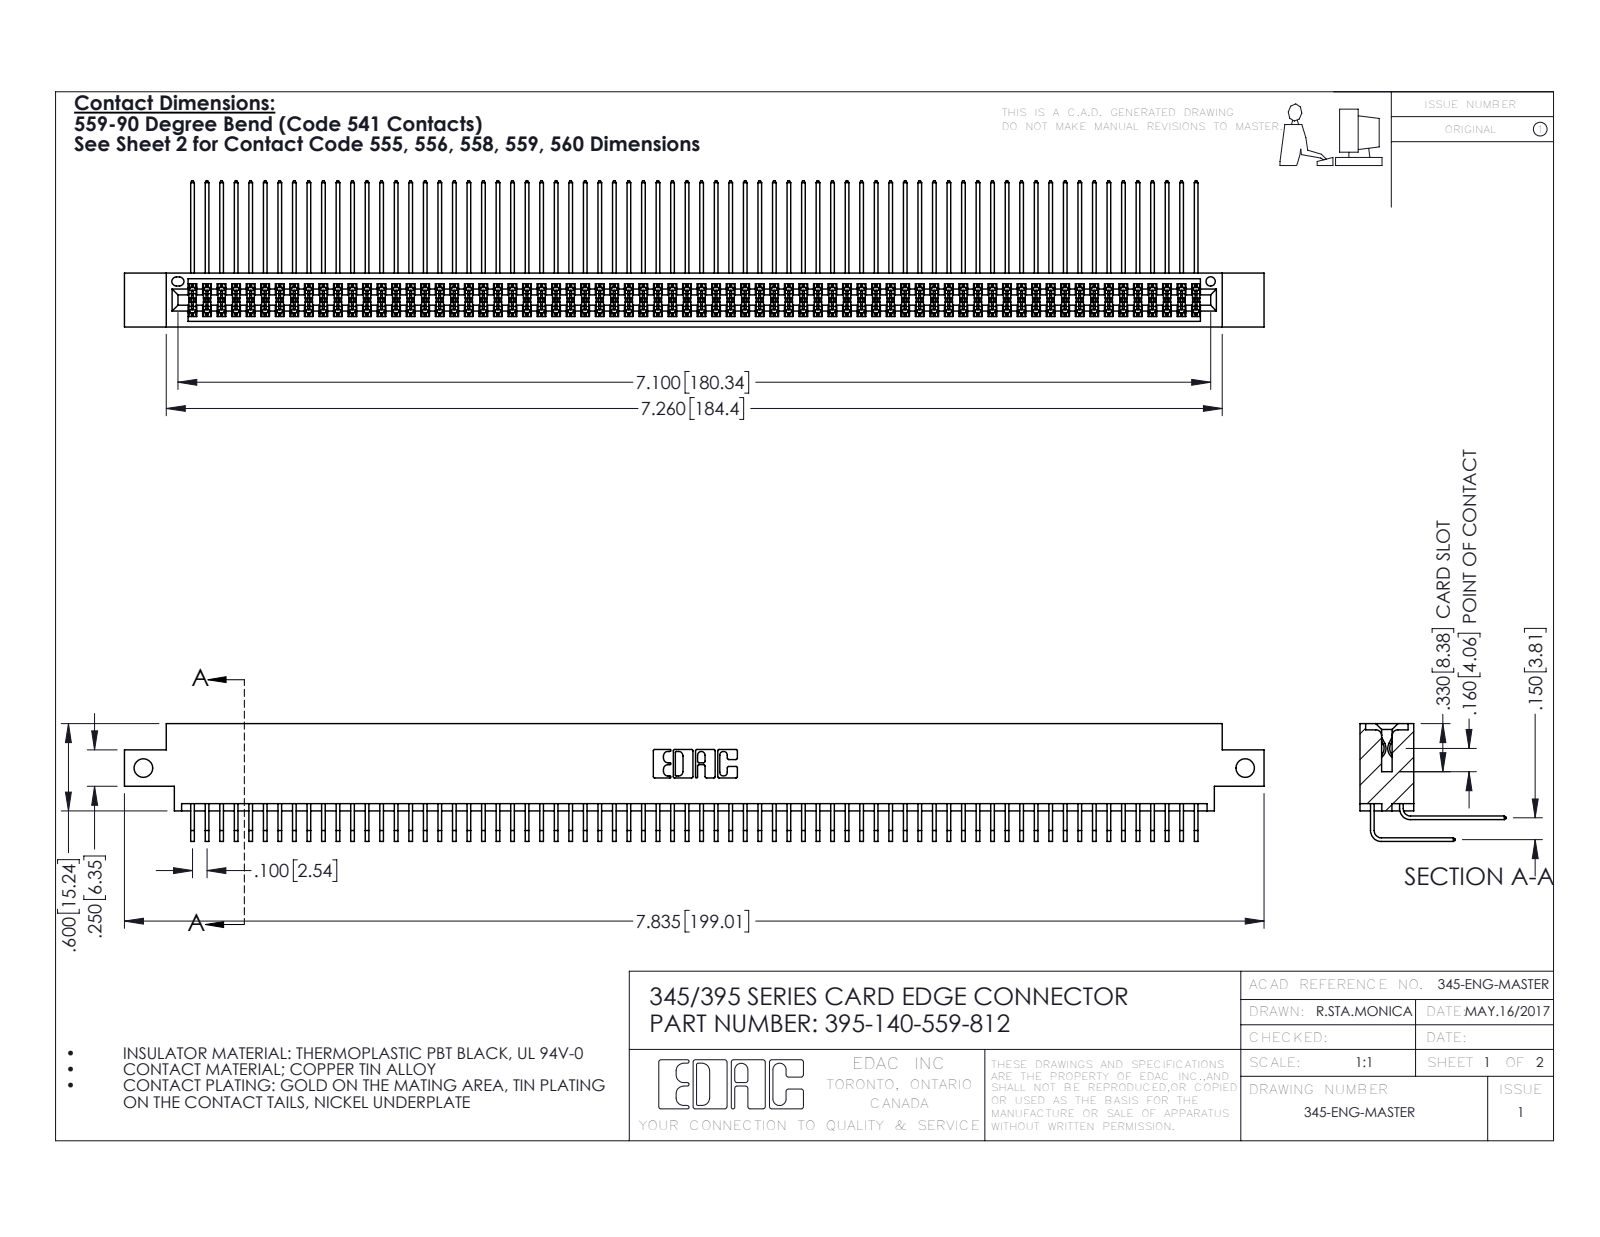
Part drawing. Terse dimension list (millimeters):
name: 345 Part_0.170 Offset - Side Mount; 395-140-559-812; 345-292-001_559 Tail - 2; 345-292-001_558 559 Tail - 1
written by: SolidWorks 2016 (CONFIG_CONTROL_DESIGN)
unit: mm
bodies: 141 solids, 7410 faces (4984 planar, 2426 cylindrical, 0 other)
size: 199 × 25.5 × 20.5
volume: 20 210 mm³; area: 34 210 mm²
holes: 2× ⌀3.3, 1× ⌀1.6
rounds: 279× R0.2, 22× R0.3, 6× R0.2, 6× R0.8, 3× R0.7, 2× R0.4, 2× R0.5, 2× R0.6
face distances: 1.8, 7.6, 9.4, 5.1, 2.5, 6.9, 0.6, 5.7, 4.4, 3.8
hole spacings: 192.4
